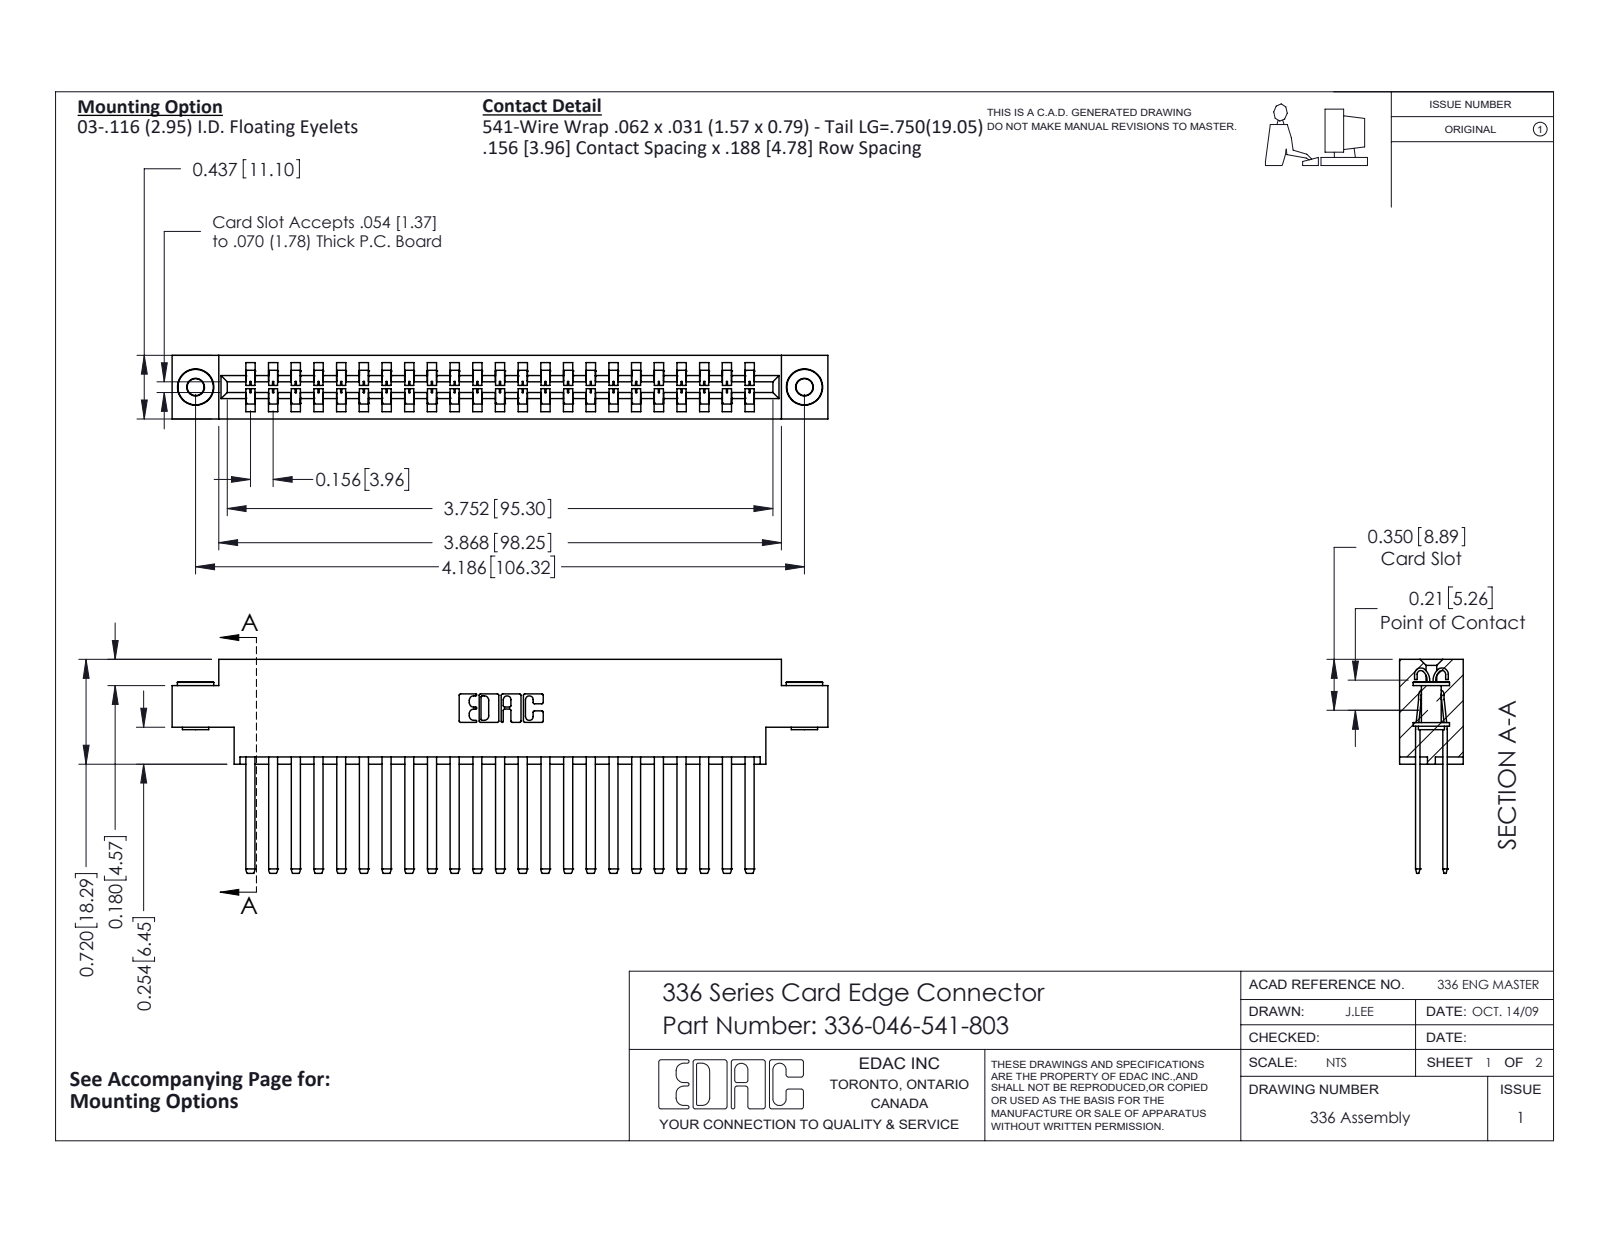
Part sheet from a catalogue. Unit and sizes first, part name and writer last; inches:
Units: inches
Overall size (bounding box): 4.509 × 1.47 × 0.437
Round holes (diameter × count): ⌀0.116 ×2, ⌀0.156 ×2
Round bosses / shafts (diameter × count): ⌀0.25 ×2, ⌀0.18 ×2, ⌀0.136 ×2
Partial cylindrical surfaces — rounded edges, fillets, slot ends (radius × count): R0.004 ×92, R0.056 ×46, R0.01 ×22, R0.007 ×6, R0.031 ×6, R0.022 ×4, R0.04 ×4, R0.026 ×3
Main face-to-face distances: 0.188, 0.031, 0.328, 0.14, 0.297, 0.109, 0.437, 0.033, 0.156, 0.181
Hole centre spacings: 4.186
Volume: 1.043 in³ · Surface area: 33.75 in²
Bodies: 49 solids, 2088 faces (1280 planar, 800 cylindrical, 8 other)
Part name (STEP PRODUCT): 336 Part_Offset - .156 Dia - TH; 336-290-001_336-290-541; 345-250-002_345-250-002-102; 336-046-541-803
STEP written by: SolidWorks 2020 (CONFIG_CONTROL_DESIGN)
